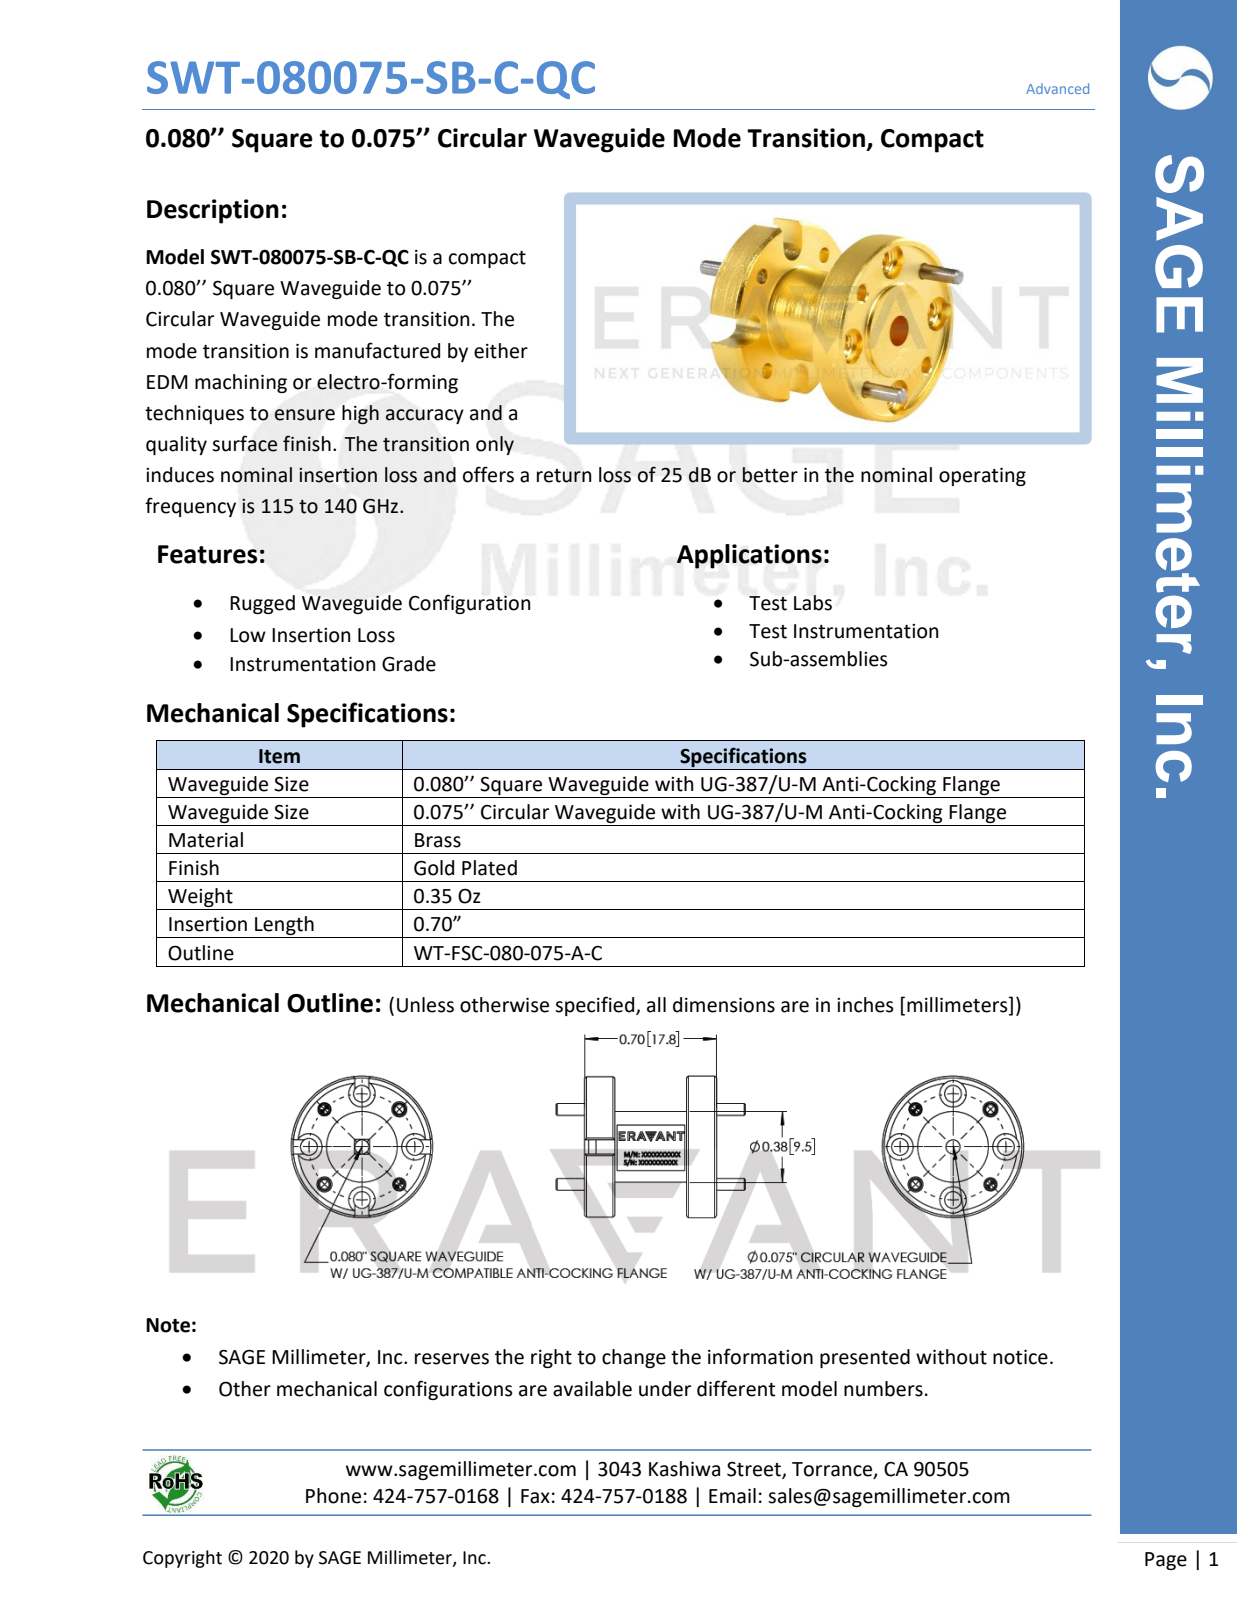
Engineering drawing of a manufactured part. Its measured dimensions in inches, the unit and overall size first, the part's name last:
Units: inches
Overall size (bounding box): 1.005 × 0.75 × 0.75
Round holes (diameter × count): ⌀0.061 ×4, ⌀0.067 ×4, ⌀0.089 ×4, ⌀0.14 ×4, ⌀0.68 ×1
Round bosses / shafts (diameter × count): ⌀0.063 ×4, ⌀0.75 ×1, ⌀0.375 ×1, ⌀0.36 ×1
Main face-to-face distances: 0.14, 0.52, 0.02, 0.16, 0.54, 0.68, 0.38, 0.66, 0.7, 0.06
Hole centre spacings: 0.215, 0.281, 0.398, 0.519, 0.562
Volume: 0.157 in³ · Surface area: 3.445 in²
Bodies: 5 solids, 175 faces (45 planar, 78 cylindrical, 52 other)
Part name (STEP PRODUCT): WT-FSC-080-075-A-C
STEP written by: SolidWorks 2021 (AUTOMOTIVE_DESIGN)
